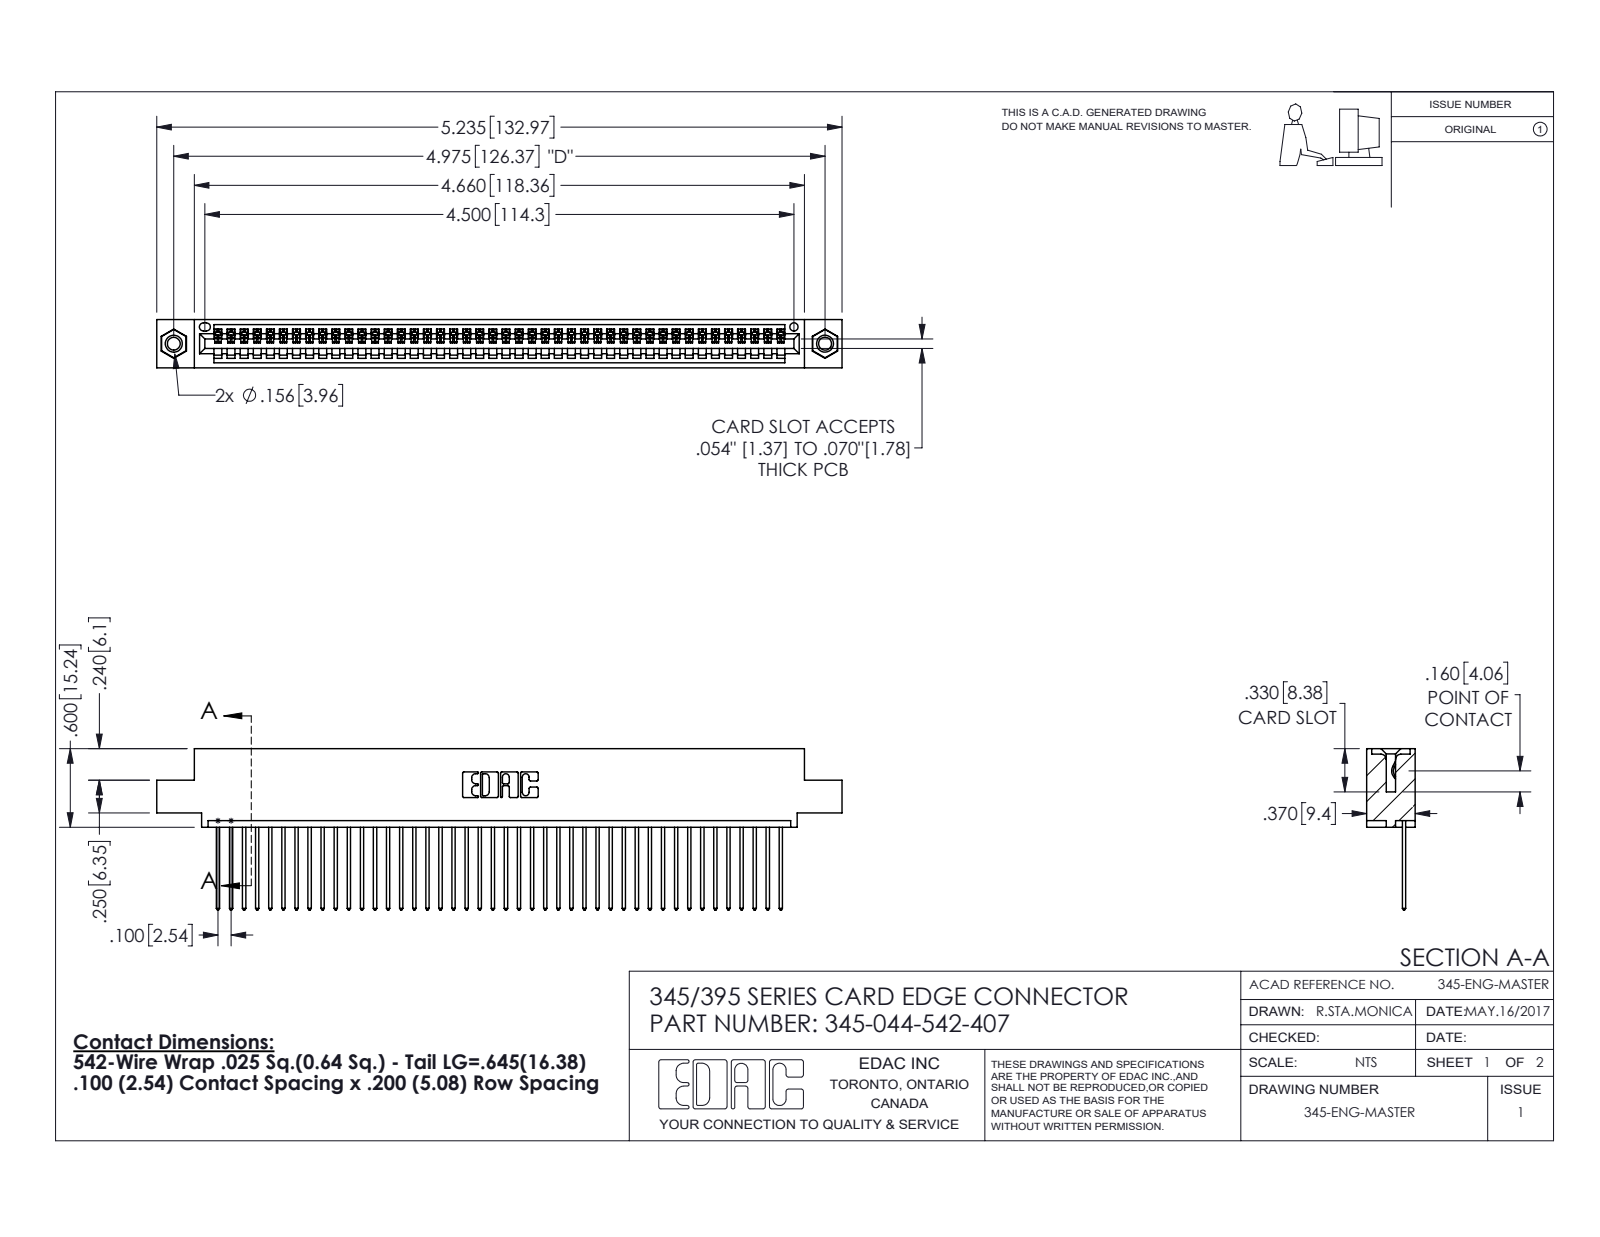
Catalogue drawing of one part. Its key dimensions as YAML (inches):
part_name: "345-292-001_345-293-142; 345-250-001_345-250-005-103; 345 Part_0.110 Offset - 0.156 Dia-TI; 345-044-542-407"
step_written_by: "SolidWorks 2016 (CONFIG_CONTROL_DESIGN)"
units: inches
bodies: {solids: 47, faces: 2742, planar: 1876, cylindrical: 850, other: 16}
overall_size: [5.235, 1.232, 0.37]
volume: 0.772
surface_area: 27.25
round_holes:
  - {diameter: 0.098, count: 2}
  - {diameter: 0.125, count: 2}
  - {diameter: 0.156, count: 2}
  - {diameter: 0.064, count: 1}
round_bosses_or_shafts:
  - {diameter: 0.155, count: 2}
partial_cylinders:
  - {radius: 0.006, count: 88}
  - {radius: 0.01, count: 88}
  - {radius: 0.01, count: 22}
  - {radius: 0.007, count: 6}
  - {radius: 0.031, count: 6}
  - {radius: 0.026, count: 3}
  - {radius: 0.031, count: 2}
  - {radius: 0.04, count: 2}
face_to_face_distances: [0.072, 0.298, 0.37, 0.098, 0.272, 0.025, 0.2, 0.225, 0.149, 0.072]
hole_center_spacings: [0.27, 4.739, 4.975]
